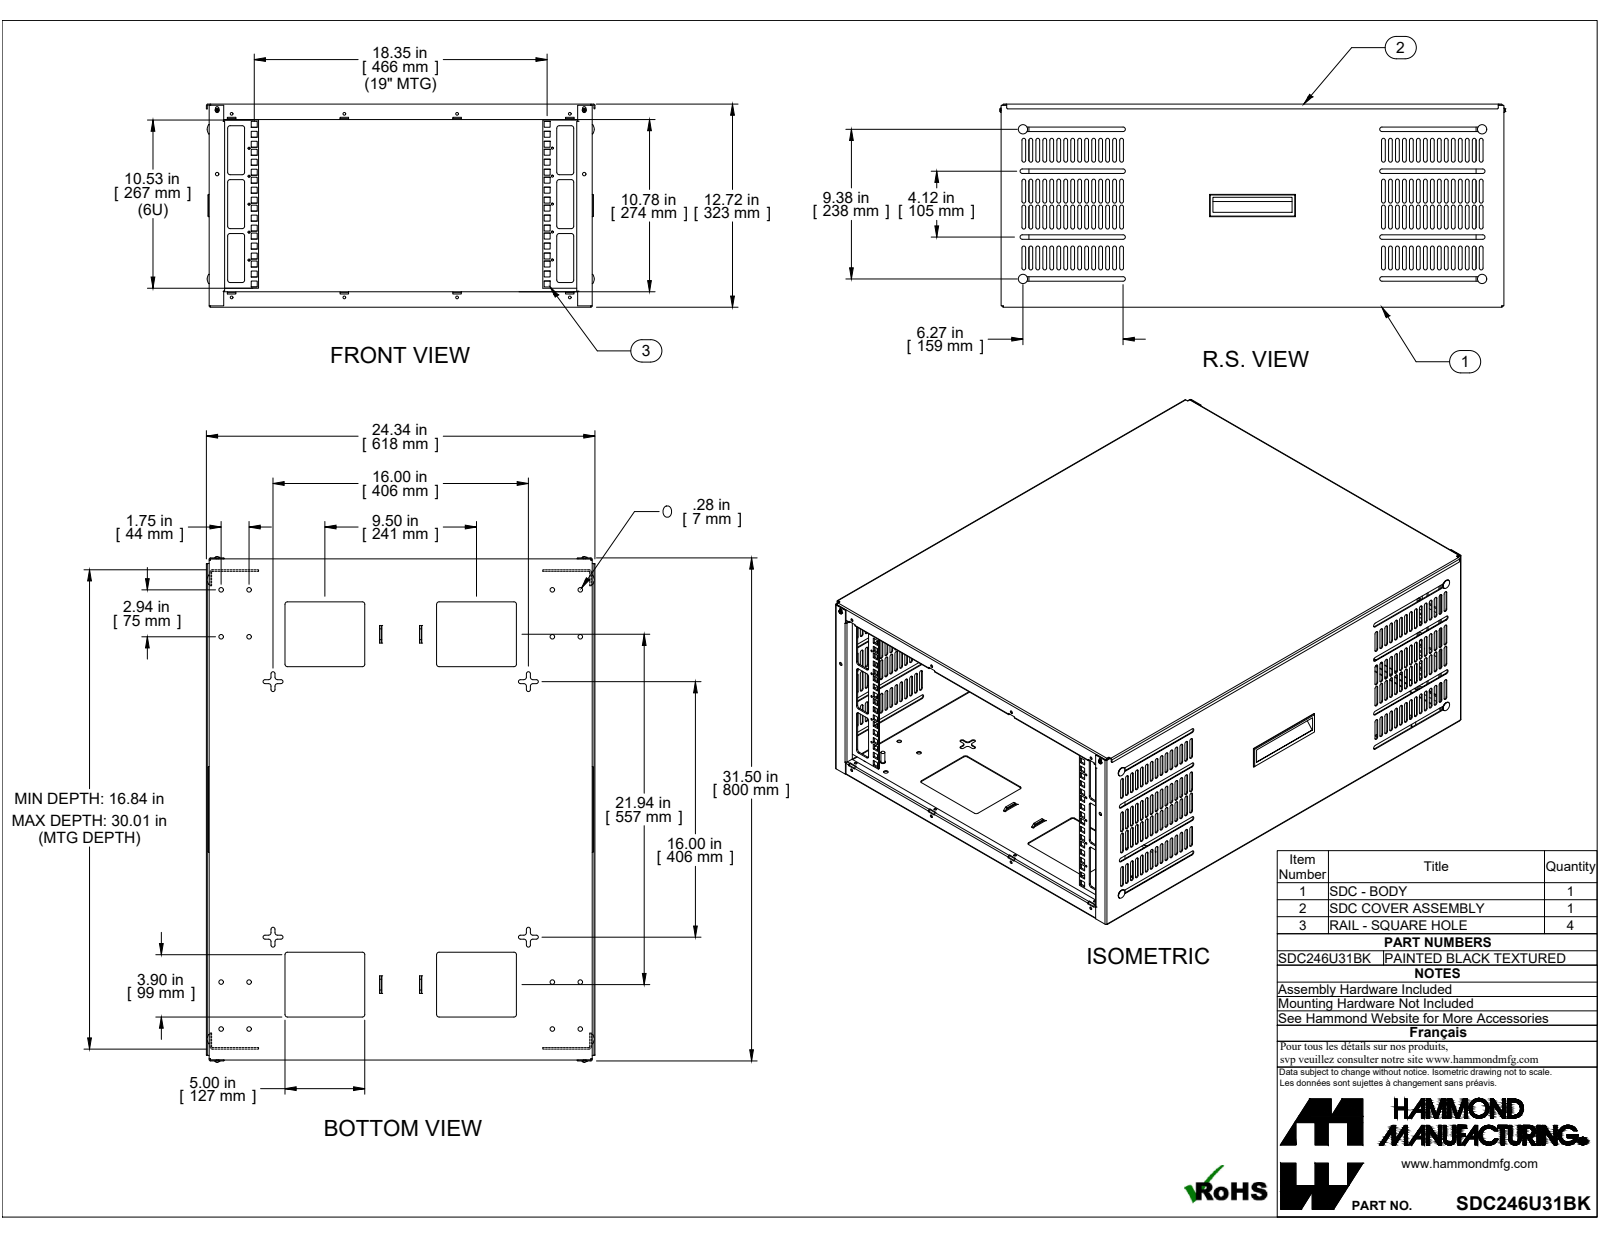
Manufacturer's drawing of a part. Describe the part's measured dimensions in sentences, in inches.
The part is named "SDC246U31BK". Its 3-D file was written by "SolidWorks 2019 (CONFIG_CONTROL_DESIGN)". It is 37 solids with 2632 faces: 1638 planar, 942 cylindrical and 52 other. Overall it measures 31.67 by 24.344 by 12.722 inches. Its volume is 153.1 cubic inches and its surface area 5 248 square inches. Round holes: 20 of diameter 0.125, 16 of diameter 0.17, 16 of diameter 0.281, 4 of diameter 0.196, 2 of diameter 0.159, 2 of diameter 0.187, 2 of diameter 0.213. Round bosses or shafts: 8 of diameter 0.25, 4 of diameter 0.58, 2 of diameter 0.313, 2 of diameter 0.28, 2 of diameter 0.187, 2 of diameter 0.138. Partial cylindrical surfaces (rounded edges, fillets, slot ends): 240 of radius 0.118, 60 of radius 0.157, 22 of radius 0.029, 22 of radius 0.086, 16 of radius 0.025, 16 of radius 0.125, 16 of radius 0.141, 14 of radius 0.117. The main face-to-face distances are 0.057, 12.665, 23.943, 12.608, 12.722, 23.886, 24, 0.072, 0.912, 12.593. The hole center spacings are 19.085, 1.75, 19.005, 19.324, 3.5, 2.937, 3.419, 7.063.
